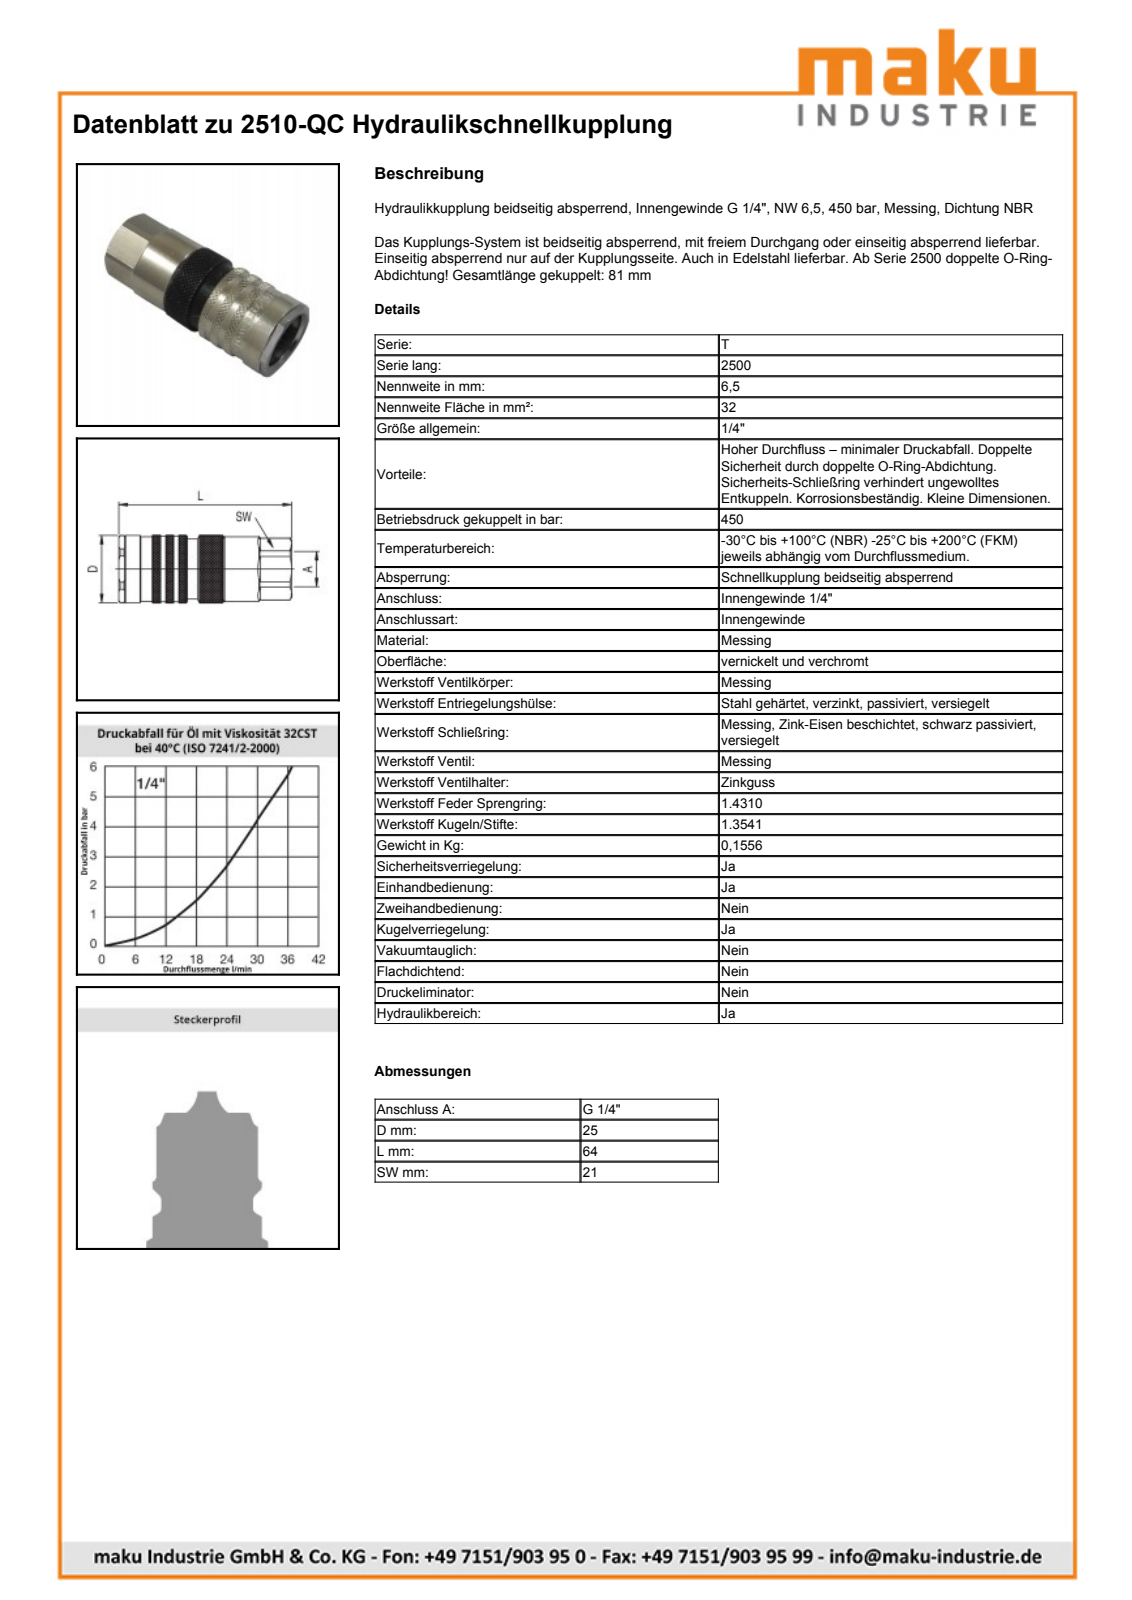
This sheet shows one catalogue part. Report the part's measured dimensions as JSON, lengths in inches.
{"part_name": "2510-QC", "step_written_by": "SolidWorks 2009 (AUTOMOTIVE_DESIGN)", "units": "inches", "bodies": {"solids": 1, "faces": 153, "planar": 21, "cylindrical": 12, "other": 120}, "overall_size": [2.504, 0.983, 0.983], "volume_in3": 1.393, "surface_area_in2": 12.98, "round_bosses_or_shafts": [[0.983, 1], [0.956, 1], [0.885, 1], [0.877, 1]], "face_to_face_distances": [0.827, 1.441, 0.189, 0.083, 1.516, 0.075, 0.106, 1.63, 1.713, 1.819]}
